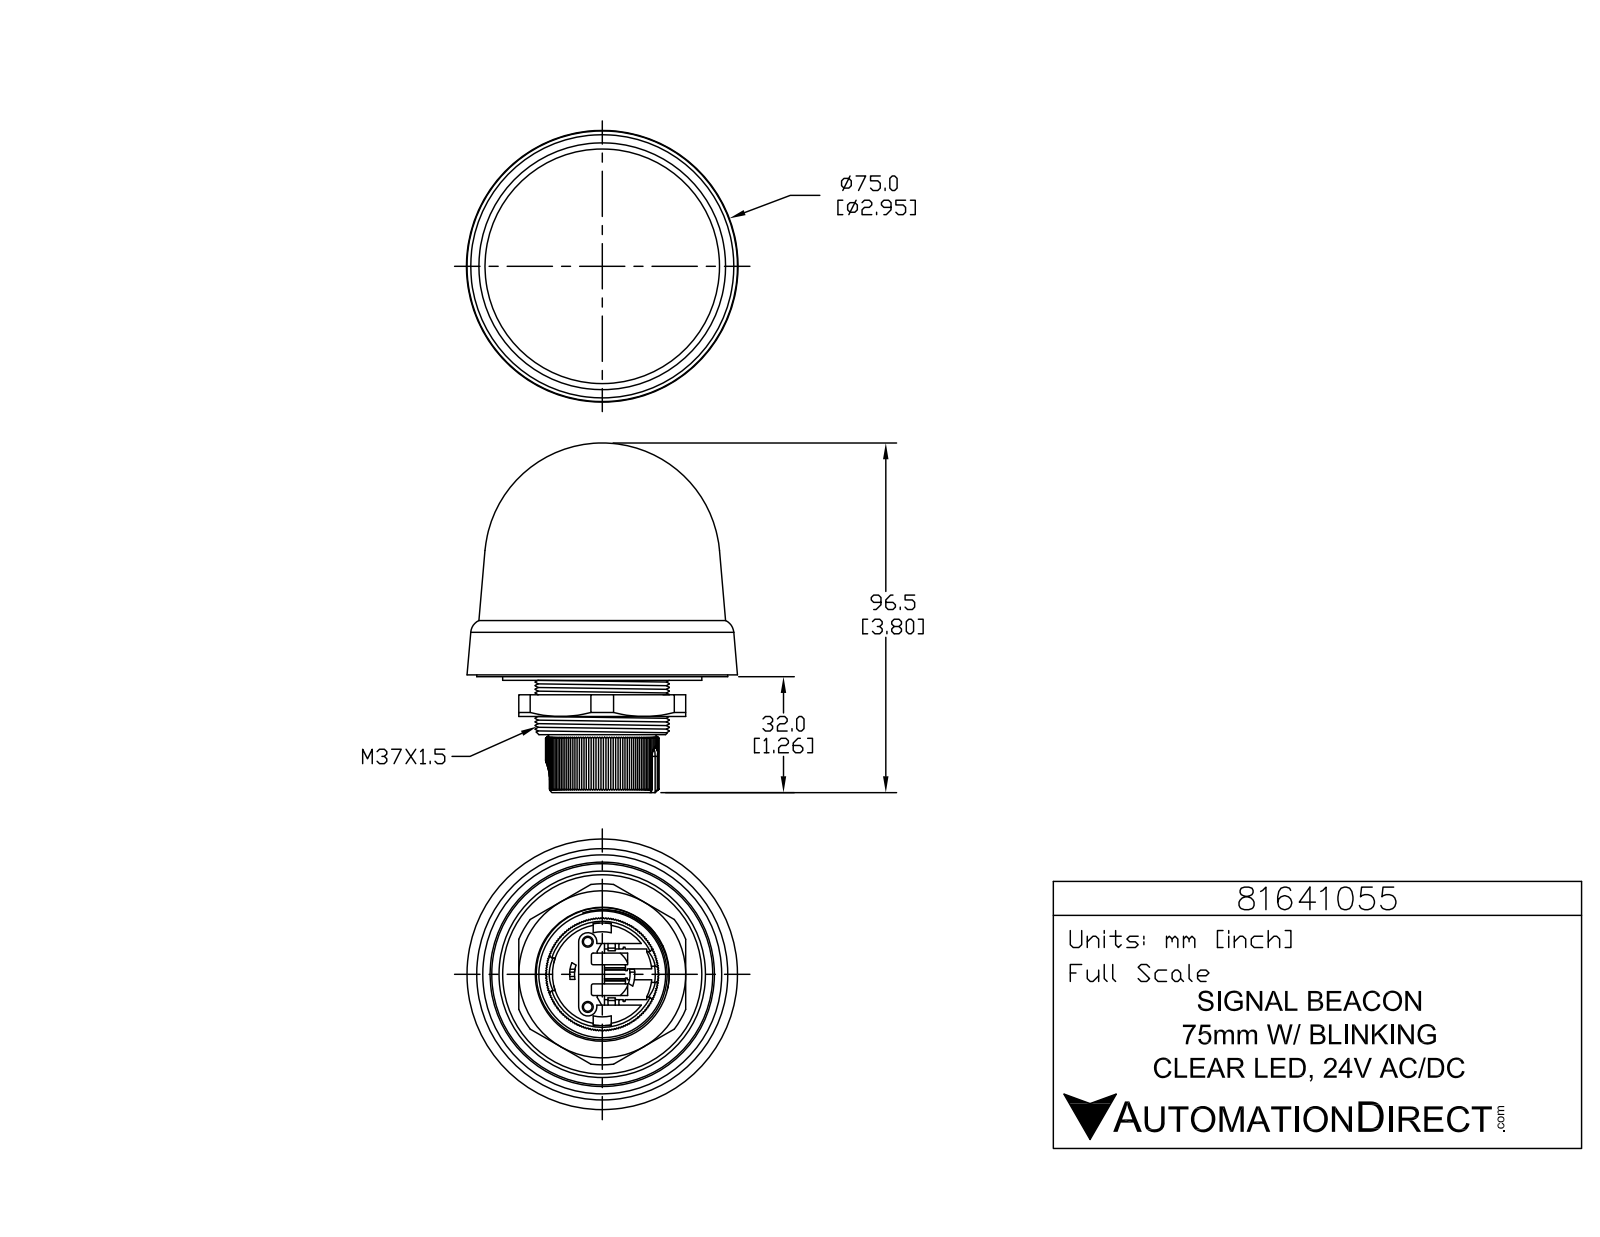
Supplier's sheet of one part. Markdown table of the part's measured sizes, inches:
| quantity | value |
| --- | --- |
| part name | 81641055 |
| STEP written by | SolidWorks 2019 (CONFIG_CONTROL_DESIGN) |
| units | inches |
| bodies | 3 solids, 560 faces (432 planar, 80 cylindrical, 48 other) |
| overall size | 3.799 × 2.941 × 2.941 |
| volume | 12.36 in³ |
| surface area | 58.68 in² |
| round holes (diameter × count) | 0.094 × 2, 0.118 × 2, 0.604 × 1, 1.142 × 1 |
| round bosses / shafts (diameter × count) | 0.217 × 2, 0.067 × 2, 2.165 × 1, 1.457 × 1, 0.925 × 1 |
| partial cylindrical surfaces (radius × count) | 0.008 × 6, 0.039 × 6, 0.02 × 4, 0.031 × 2, 0.079 × 2, 0.098 × 2, 0.177 × 1, 0.354 × 1 |
| main face-to-face distances | 0.177, 0.354, 0.197, 0.433, 0.512, 0.335, 0.059, 0.394, 0.118, 0.157 |
| hole center spacings | 0.388, 0.709 |
